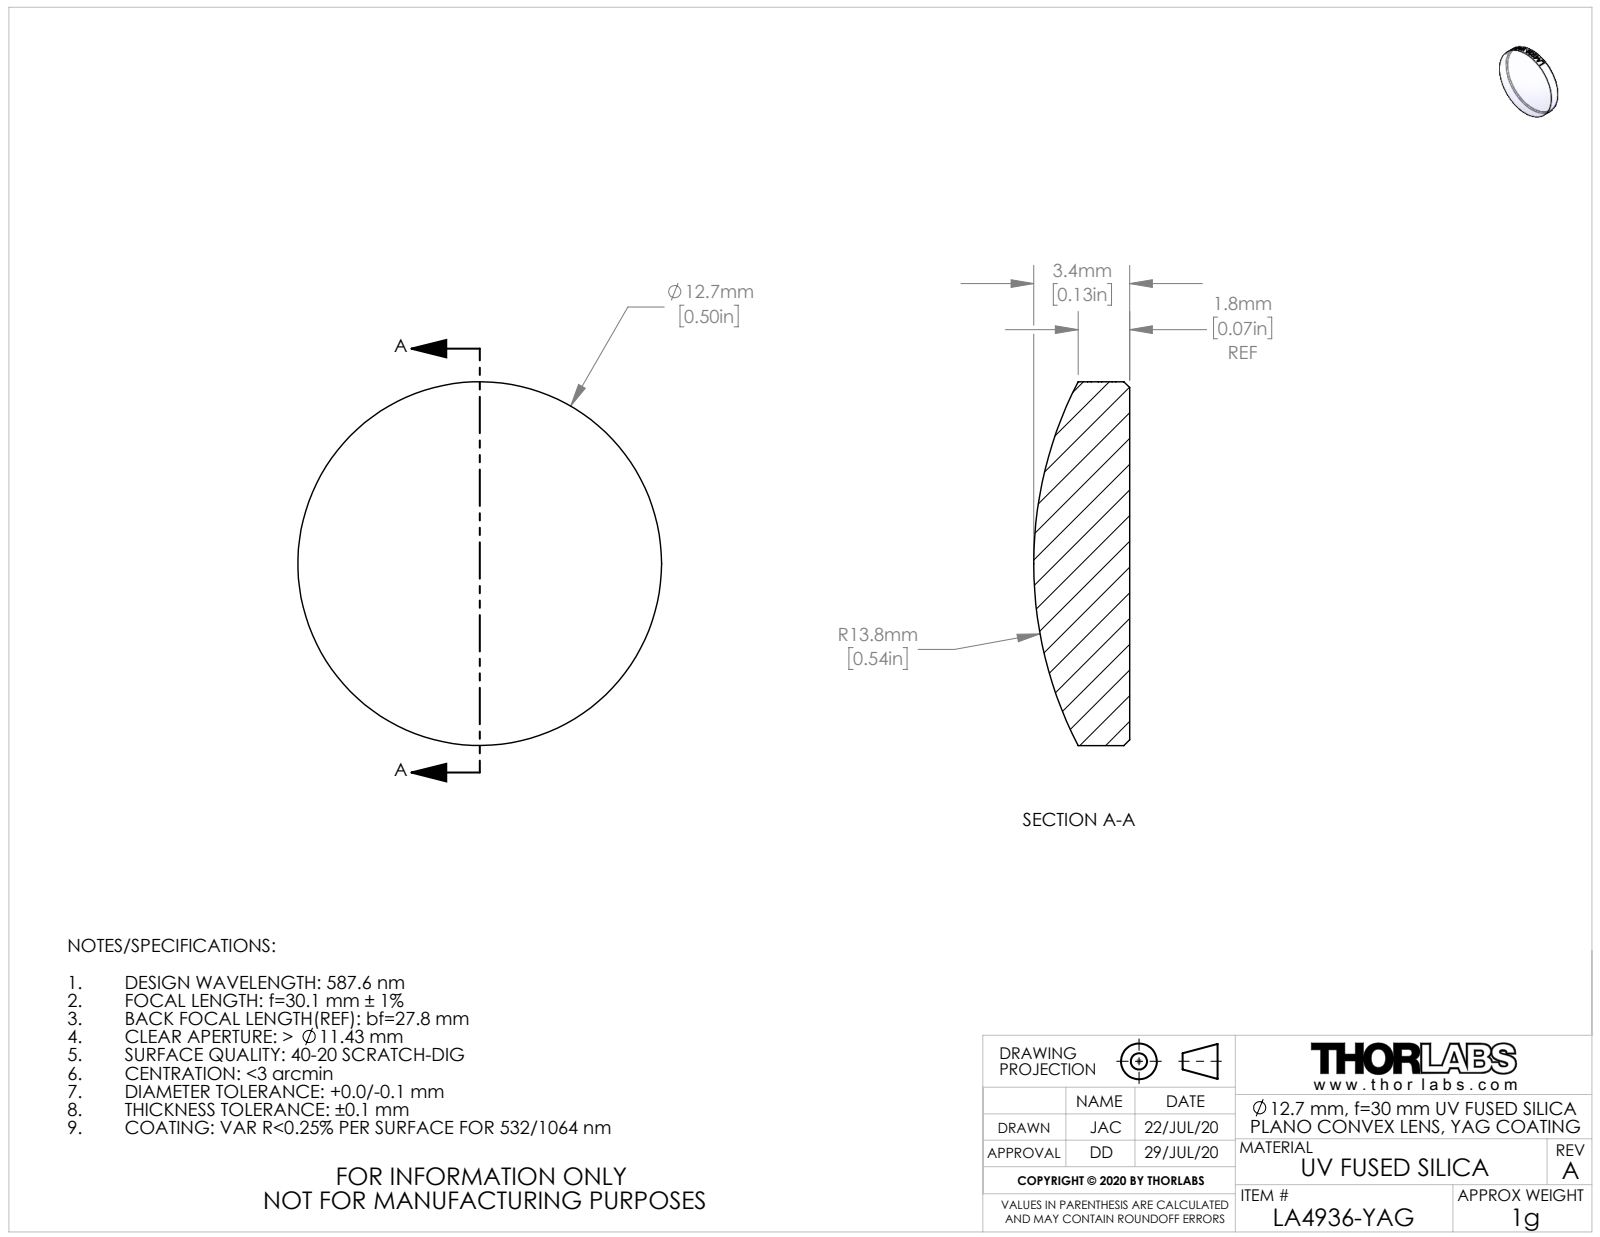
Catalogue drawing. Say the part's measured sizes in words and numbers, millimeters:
The part is named "TTN217847-E0W". Its 3-D file was written by "SolidWorks 2018 (CONFIG_CONTROL_DESIGN)". It is 1 solid with 26 faces: 1 planar, 21 cylindrical and 4 other. Overall it measures 12.7 by 12.7 by 3.4 millimeters. Its volume is 330 cubic millimeters and its surface area 328 square millimeters. Round bosses or shafts: 1 of diameter 12.7.
